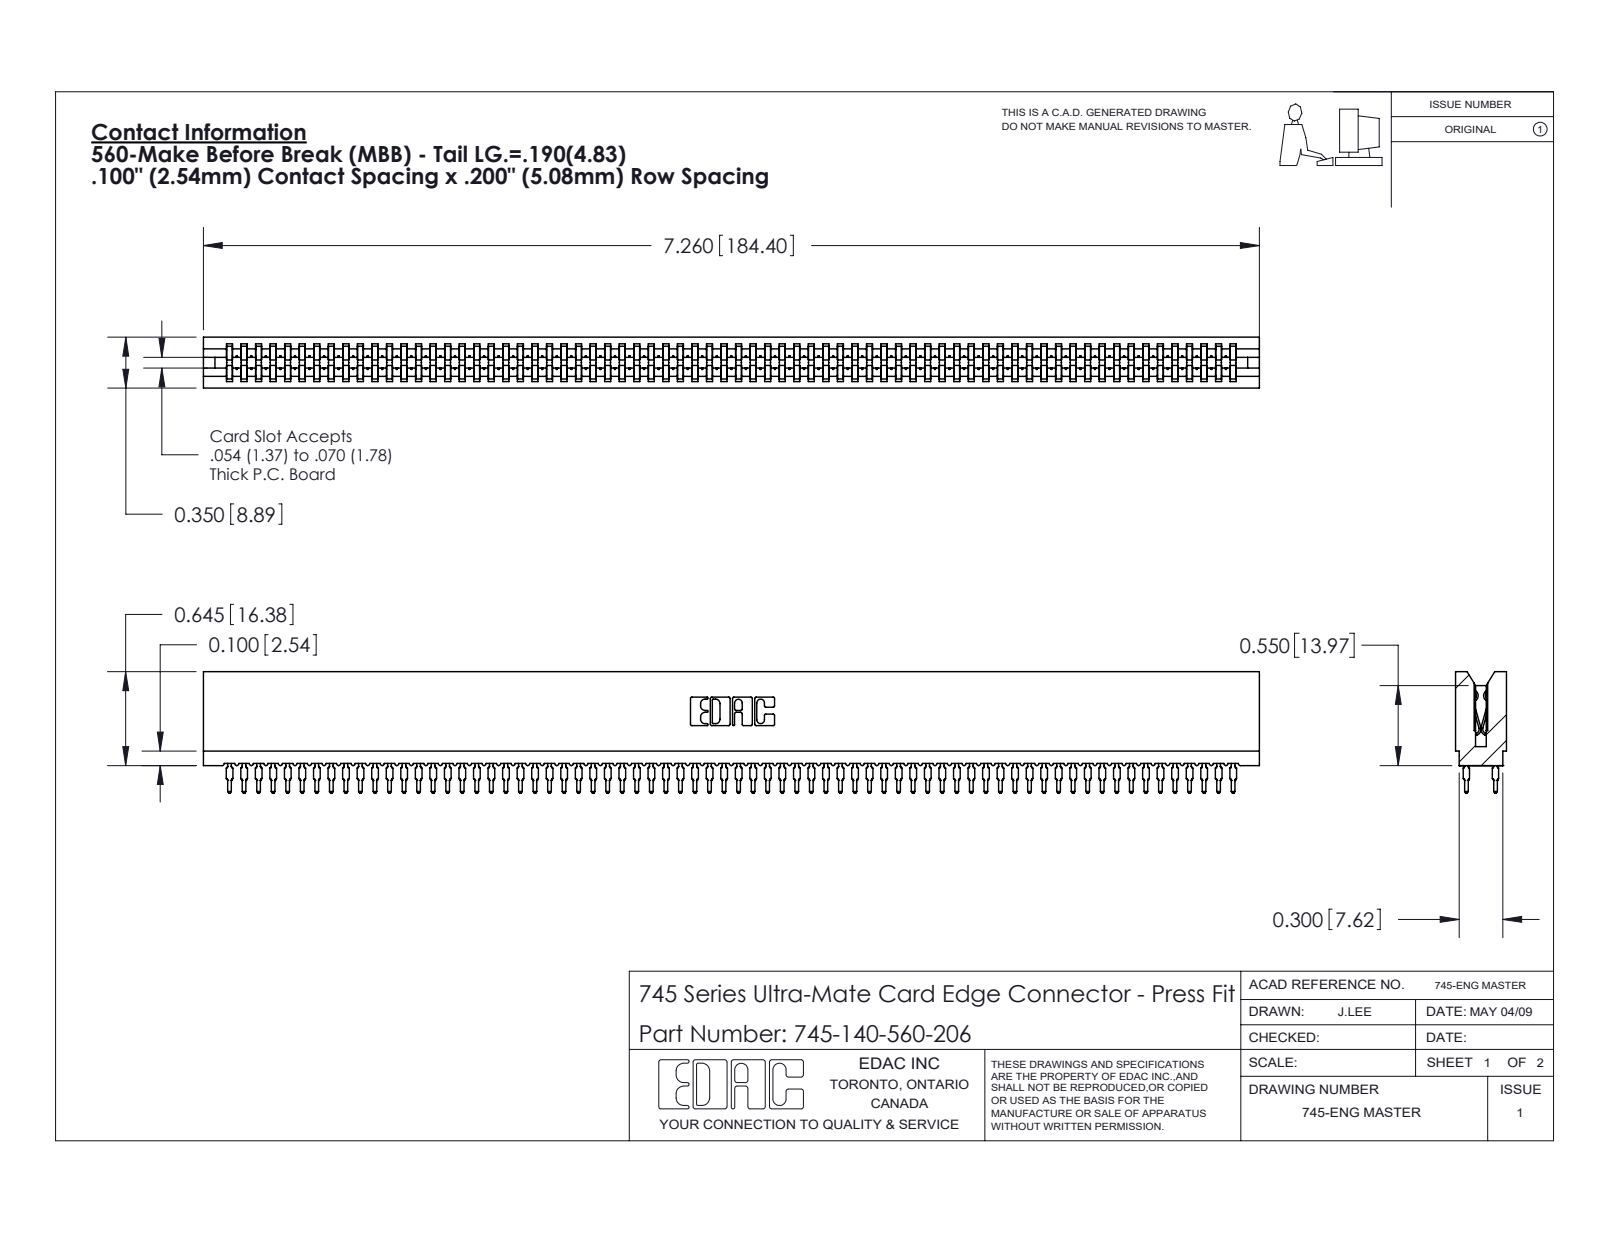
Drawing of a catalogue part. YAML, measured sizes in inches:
part_name: "745-140-560-206; 745 Part_Insulator Option - 06; 745-292-001_560"
step_written_by: "SolidWorks 2020 (CONFIG_CONTROL_DESIGN)"
units: inches
bodies: {solids: 141, faces: 13886, planar: 7196, cylindrical: 3050, other: 3640}
overall_size: [7.26, 0.836, 0.35]
volume: 1.033
surface_area: 57.83
partial_cylinders:
  - {radius: 0.021, count: 280}
  - {radius: 0.015, count: 140}
  - {radius: 0.01, count: 22}
  - {radius: 0.005, count: 8}
  - {radius: 0.011, count: 8}
  - {radius: 0.007, count: 6}
  - {radius: 0.031, count: 6}
  - {radius: 0.026, count: 3}
face_to_face_distances: [0.35, 0.063, 0.287, 0.045, 0.305, 0.018, 0.243, 0.138, 0.212, 0.093]
